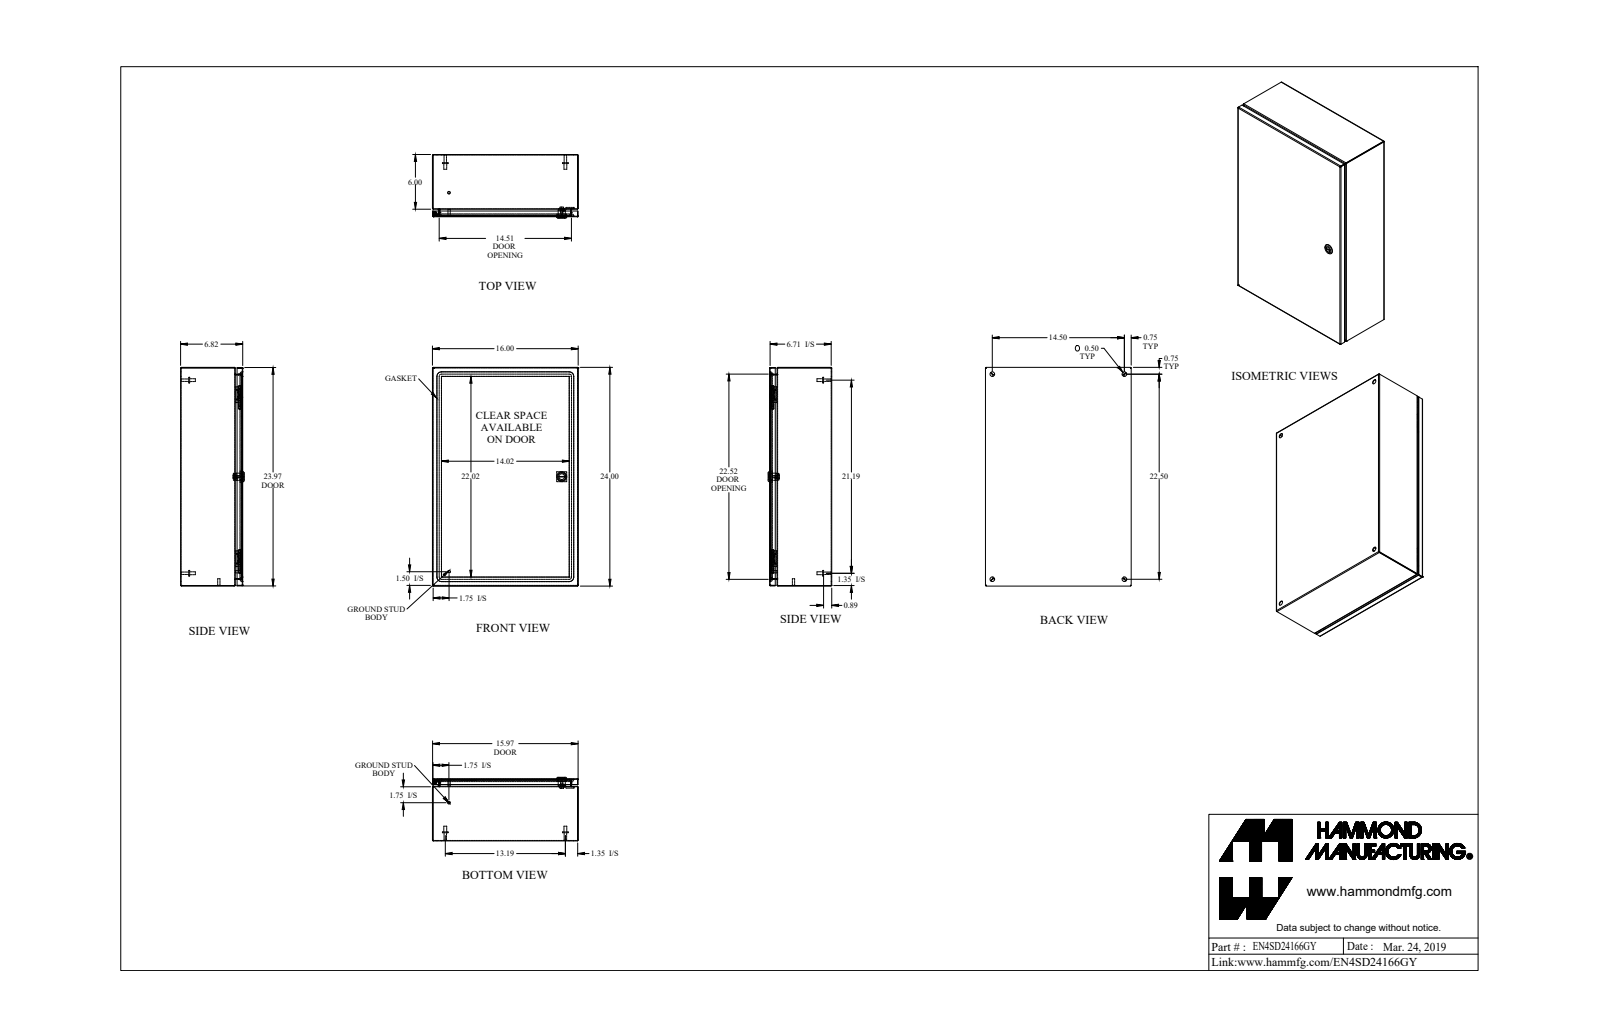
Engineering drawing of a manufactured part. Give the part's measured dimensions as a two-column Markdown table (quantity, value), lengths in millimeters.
| quantity | value |
| --- | --- |
| part name | EN4SD24166GY_Default |
| STEP written by | SolidWorks 2019 (CONFIG_CONTROL_DESIGN) |
| units | millimeters |
| bodies | 21 solids, 634 faces (285 planar, 213 cylindrical, 136 other) |
| overall size | 609.6 × 406.4 × 177.3 |
| volume | 1 441 000 mm³ |
| surface area | 1 926 000 mm² |
| round holes (diameter × count) | 12.7 × 4, 4.4 × 1, 5.9 × 1, 6.1 × 1, 6.1 × 1, 15.9 × 1, 19.9 × 1 |
| round bosses / shafts (diameter × count) | 15.9 × 4, 8 × 4, 6.9 × 4, 7.1 × 2, 6.4 × 2, 27.9 × 1, 13.3 × 1, 11.6 × 1 |
| partial cylindrical surfaces (radius × count) | 0.7 × 21, 2.2 × 21, 6.4 × 16, 482.6 × 8, 0.2 × 4, 1.6 × 4, 12.7 × 4, 3.2 × 2 |
| main face-to-face distances | 1.4, 171.8, 170.4, 173.3, 405, 608.2, 403.5, 406.4, 20.9, 151 |
| hole center spacings | 368.3, 571.5, 679.9, 287, 287, 445.2, 445.2 |
